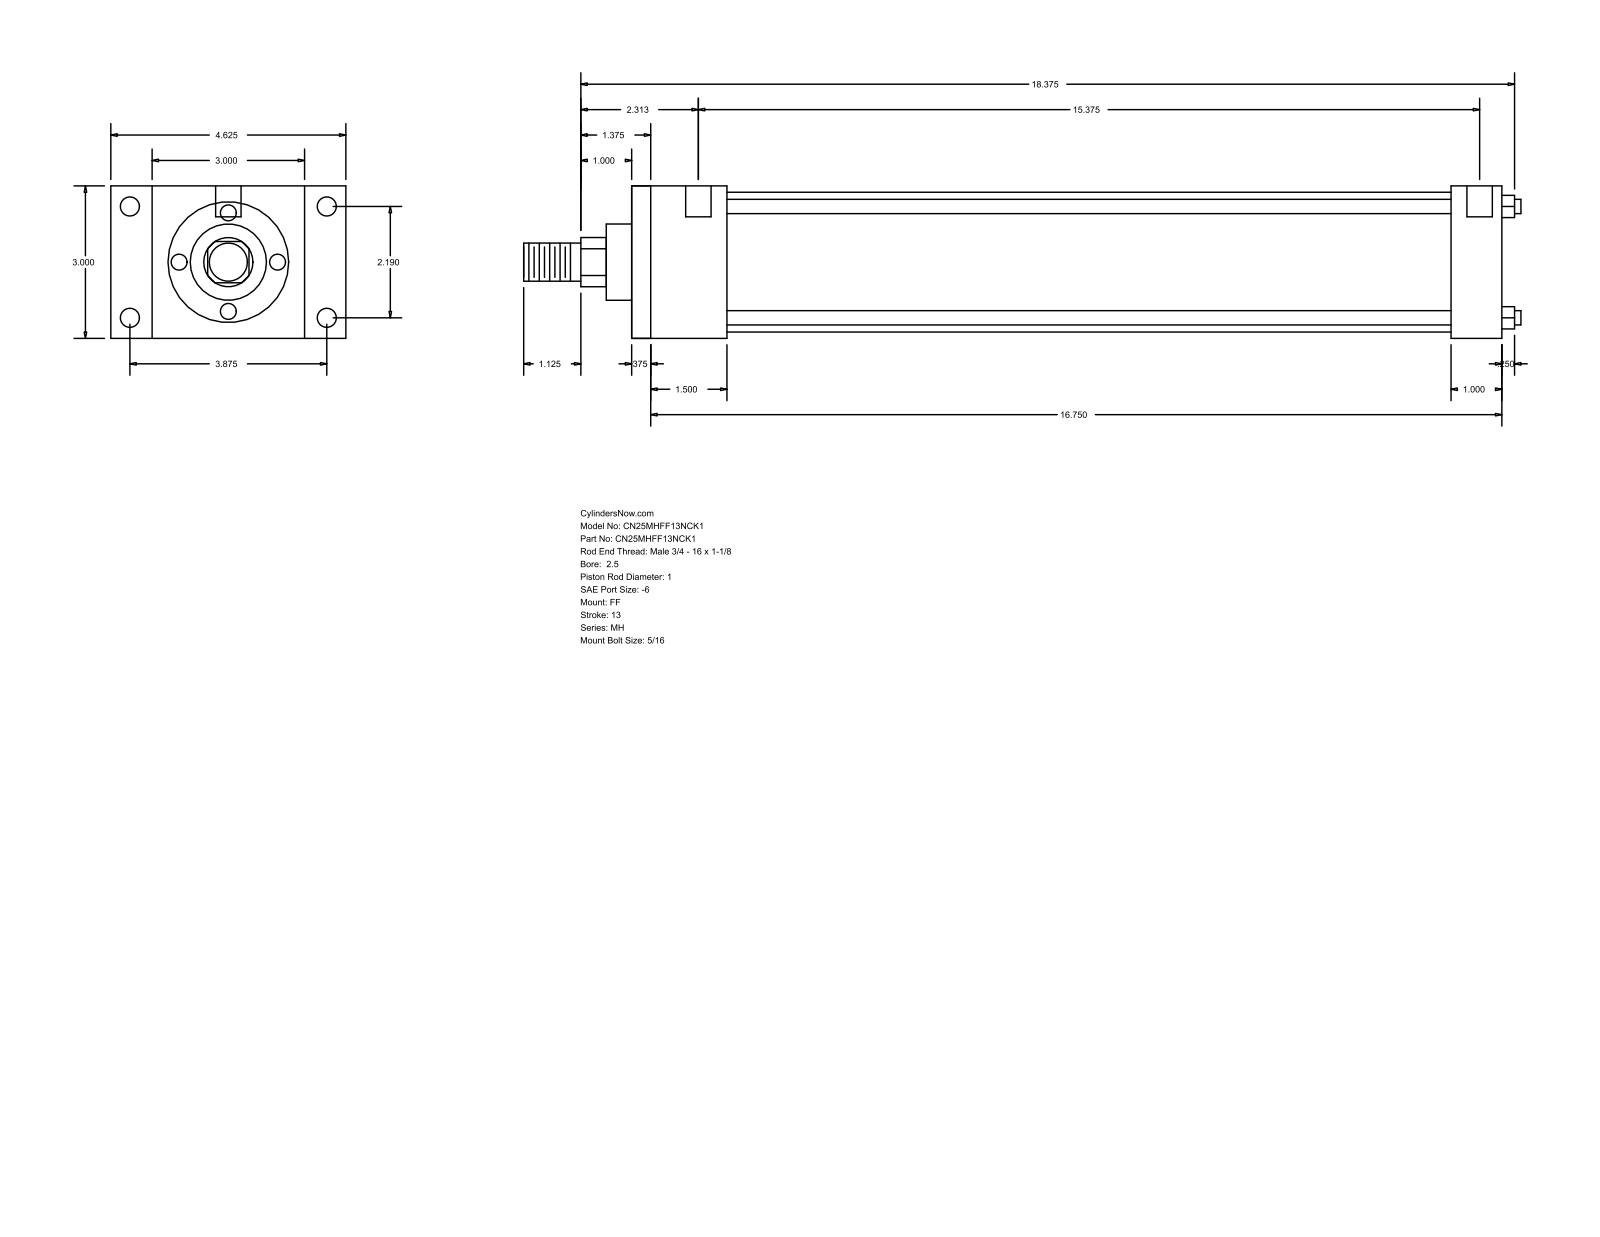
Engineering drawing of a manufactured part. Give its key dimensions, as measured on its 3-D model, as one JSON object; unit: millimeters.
{"part_name": "MH_FF__0250_1", "step_written_by": "GSSL Pune (CONFIG_CONTROL_DESIGN)", "units": "millimeters", "bodies": {"solids": 0, "faces": 92, "planar": 64, "cylindrical": 28, "other": 0}, "overall_size": [498.48, 117.47, 76.2], "round_holes": [[5.56, 4], [9.53, 4], [12.7, 2]], "round_bosses_or_shafts": [[7.14, 4], [69.85, 1], [38.1, 1], [25.4, 1], [19.05, 1]], "partial_cylinders_radius": [[12.29, 1]], "face_to_face_distances": [76.2, 434.98, 9.52, 425.46, 25.4, 47.63, 409.58, 38.11, 400.06, 361.95], "hole_center_spacings": [55.62, 98.42, 113.05, 398.46, 3.18, 4.76, 390.52, 393.7]}
